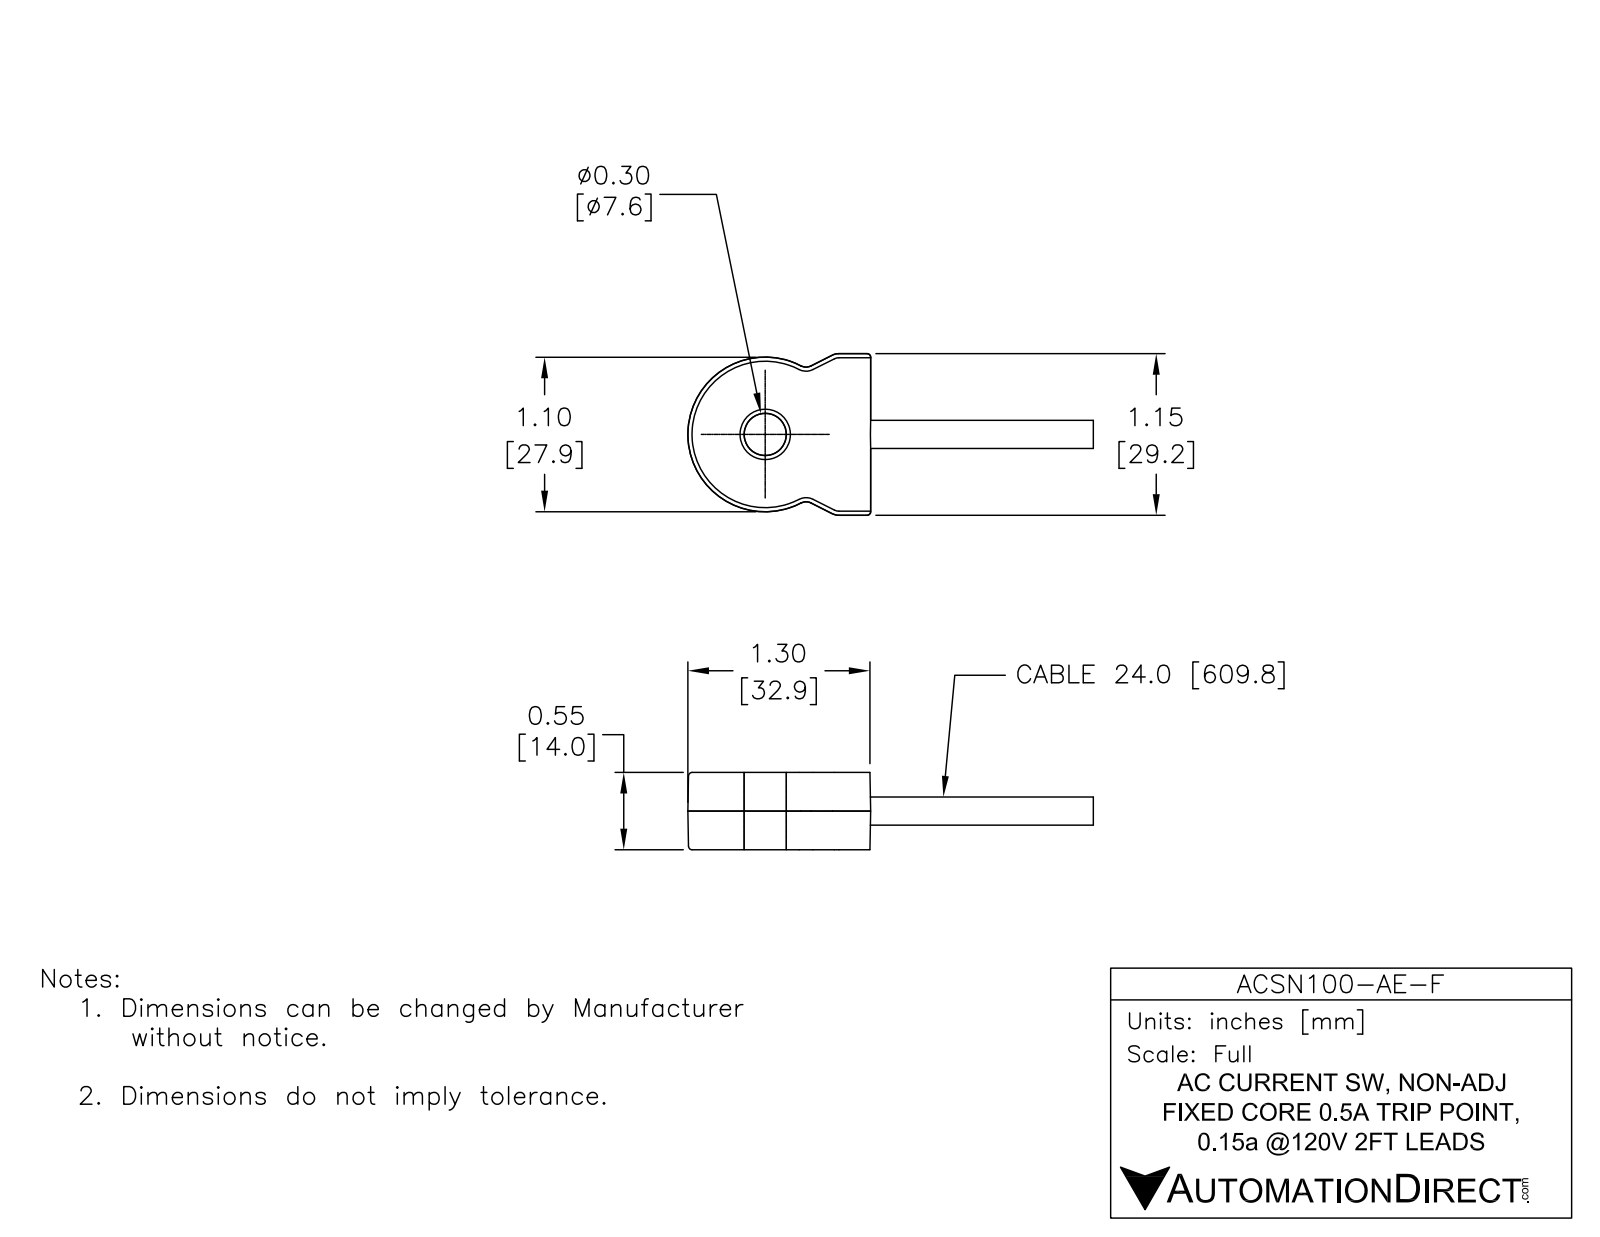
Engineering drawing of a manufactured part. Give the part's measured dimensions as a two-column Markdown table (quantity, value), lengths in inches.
| quantity | value |
| --- | --- |
| part name | ACSN100-AE-F |
| STEP written by | SolidWorks 2014 (AUTOMOTIVE_DESIGN) |
| units | inches |
| bodies | 3 solids, 74 faces (15 planar, 27 cylindrical, 32 other) |
| overall size | 2.783 × 1.158 × 0.568 |
| volume | 0.705 in³ |
| surface area | 6.306 in² |
| round holes (diameter × count) | 0.159 × 1, 0.307 × 1 |
| round bosses / shafts (diameter × count) | 0.079 × 2, 0.323 × 1 |
| partial cylindrical surfaces (radius × count) | 0.016 × 16, 0.553 × 1 |
| main face-to-face distances | 0.567, 1.158, 0.055, 0.201, 0.203 |
